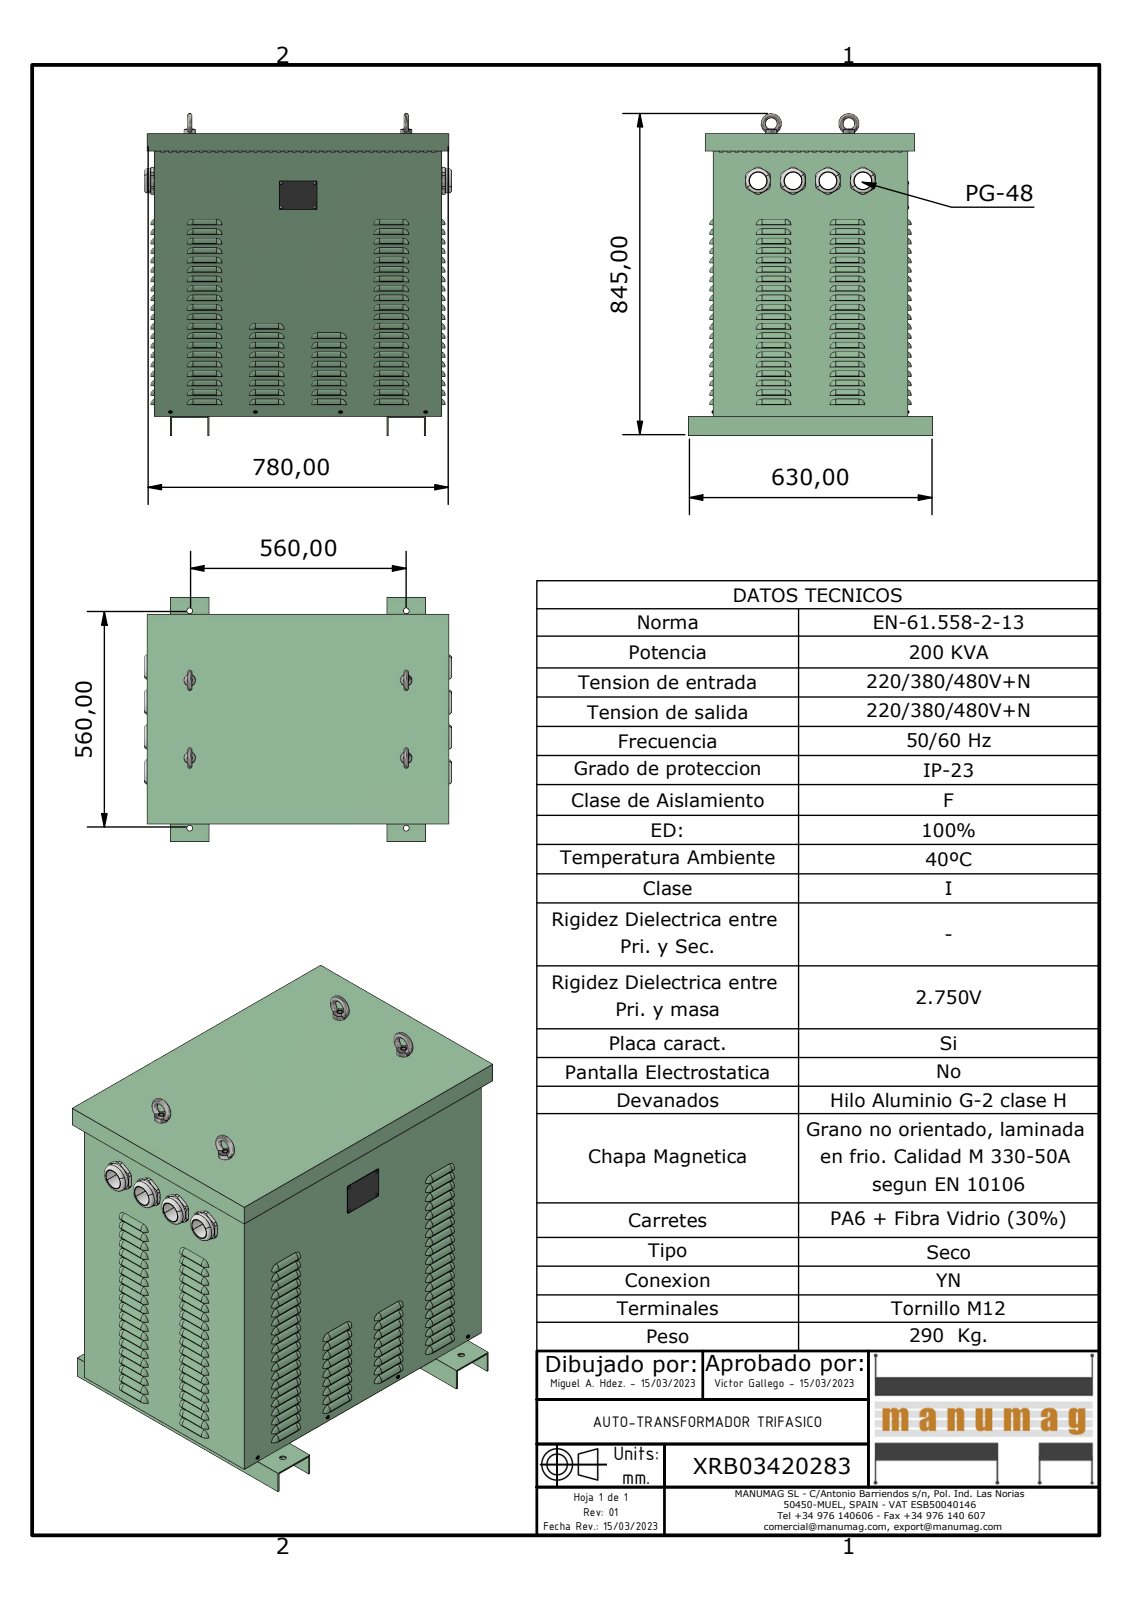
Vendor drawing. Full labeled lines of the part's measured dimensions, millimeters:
Part name (STEP PRODUCT): XRB03420283; JE200 CUERPO; JE160 EXPORT JE200 EXPORT NACIONAL BASE; JE160 EXPORT JE200 EXPORT NACIONAL PATA (+6 more)
STEP written by: Autodesk Inventor 2023 (AUTOMOTIVE_DESIGN)
Units: millimetres
Bodies: 30 solids, 4663 faces (1571 planar, 1992 cylindrical, 1100 other)
Overall size (bounding box): 835 × 795.27 × 630
Volume: 7 588 000 mm³ · Surface area: 6 374 000 mm²
Round holes (diameter × count): ⌀11 ×936, ⌀15 ×12, ⌀4 ×4, ⌀5 ×4, ⌀10.11 ×4, ⌀44 ×4, ⌀60 ×4
Round bosses / shafts (diameter × count): ⌀63 ×4, ⌀59.3 ×4, ⌀59.15 ×4, ⌀57.63 ×4, ⌀30 ×4, ⌀4 ×4, ⌀3.62 ×4, ⌀3.2 ×4
Partial cylindrical surfaces — rounded edges, fillets, slot ends (radius × count): R14 ×194, R7 ×80, R15 ×80, R2.5 ×8, R2 ×4, R35 ×4
Main face-to-face distances: 2, 500, 730, 742, 498, 502, 732, 740, 728, 744
Hole centre spacings: 15, 30, 33.54, 204.55, 159.71, 204, 129.87, 159
